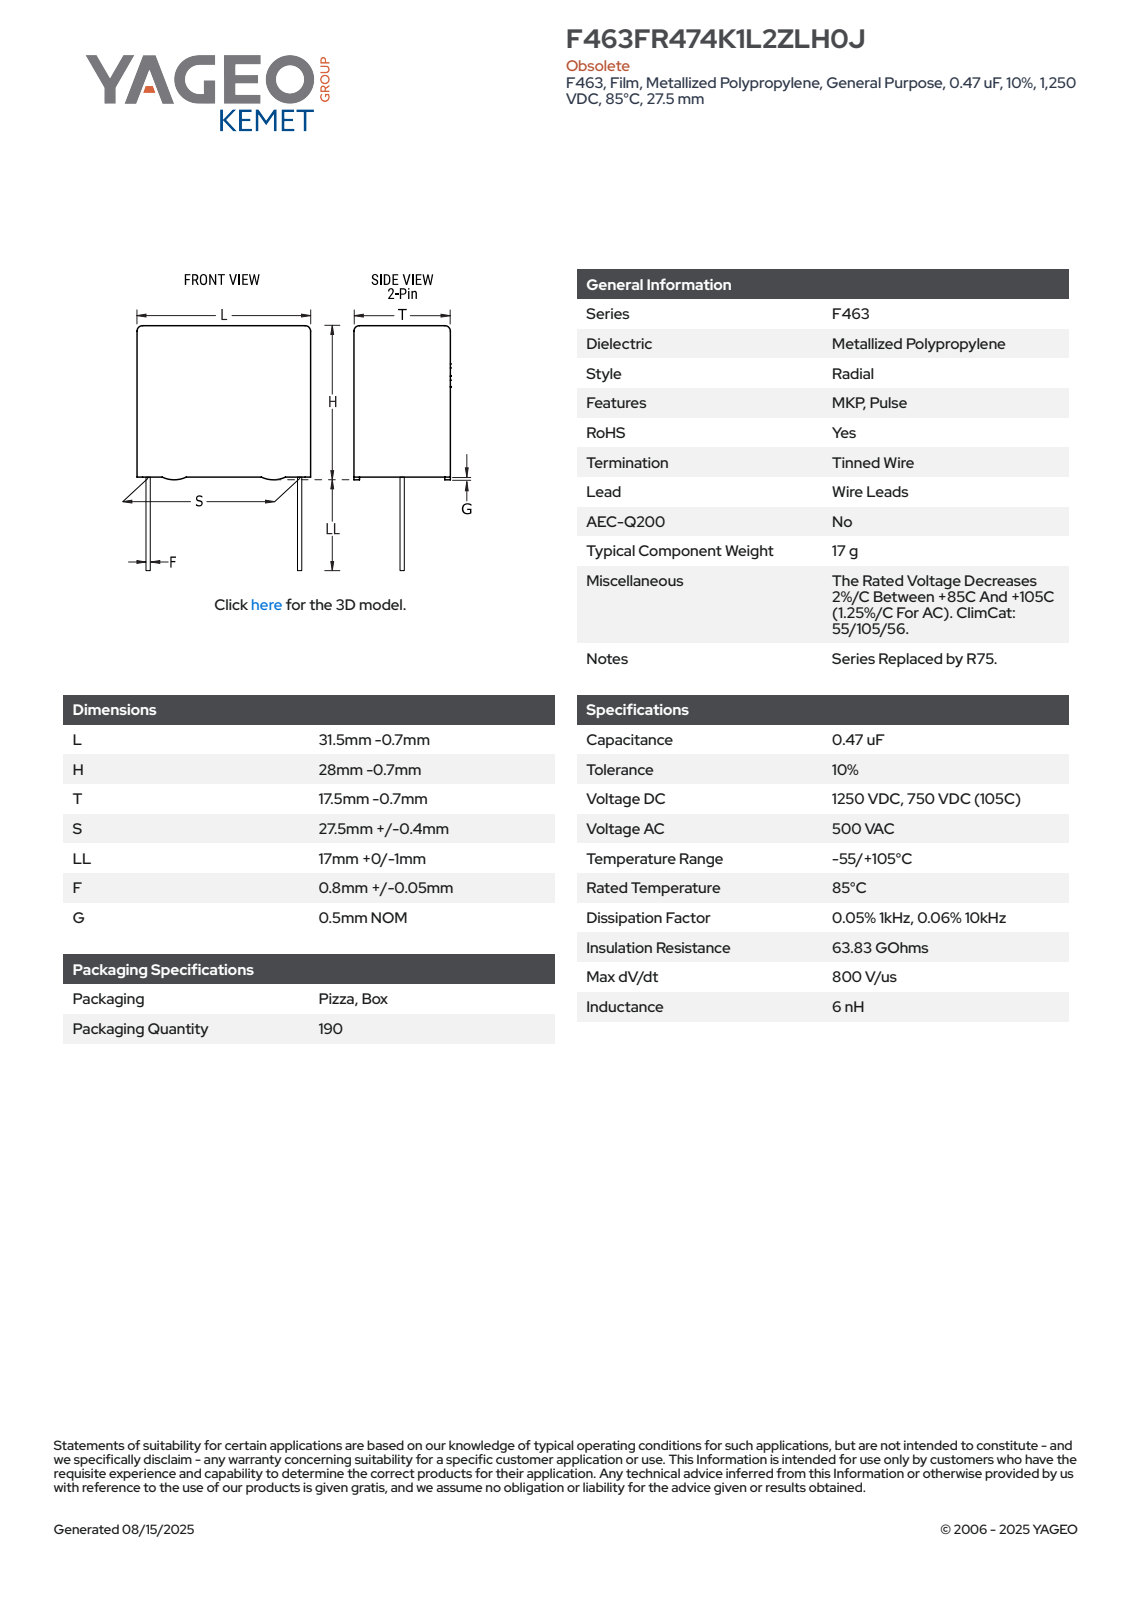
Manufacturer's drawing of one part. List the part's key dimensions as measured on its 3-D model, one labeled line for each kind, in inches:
Part name (STEP PRODUCT): CFR_RBG_31.5X28X17.5_L30.8H27.3T16.8S27.5LL17F0.85G0.5
STEP written by: SolidWorks 2014 (AUTOMOTIVE_DESIGN)
Units: inches
Bodies: 4 solids, 89 faces (81 planar, 8 cylindrical, 0 other)
Overall size (bounding box): 1.744 × 1.213 × 0.661
Volume: 0.848 in³ · Surface area: 5.865 in²
Round bosses / shafts (diameter × count): ⌀0.033 ×2
Partial cylindrical surfaces — rounded edges, fillets, slot ends (radius × count): R0.02 ×4
Main face-to-face distances: 0.661, 1.055, 1.213, 0.662, 0.02, 1.075, 0.038, 0.624, 0.038, 0.586
